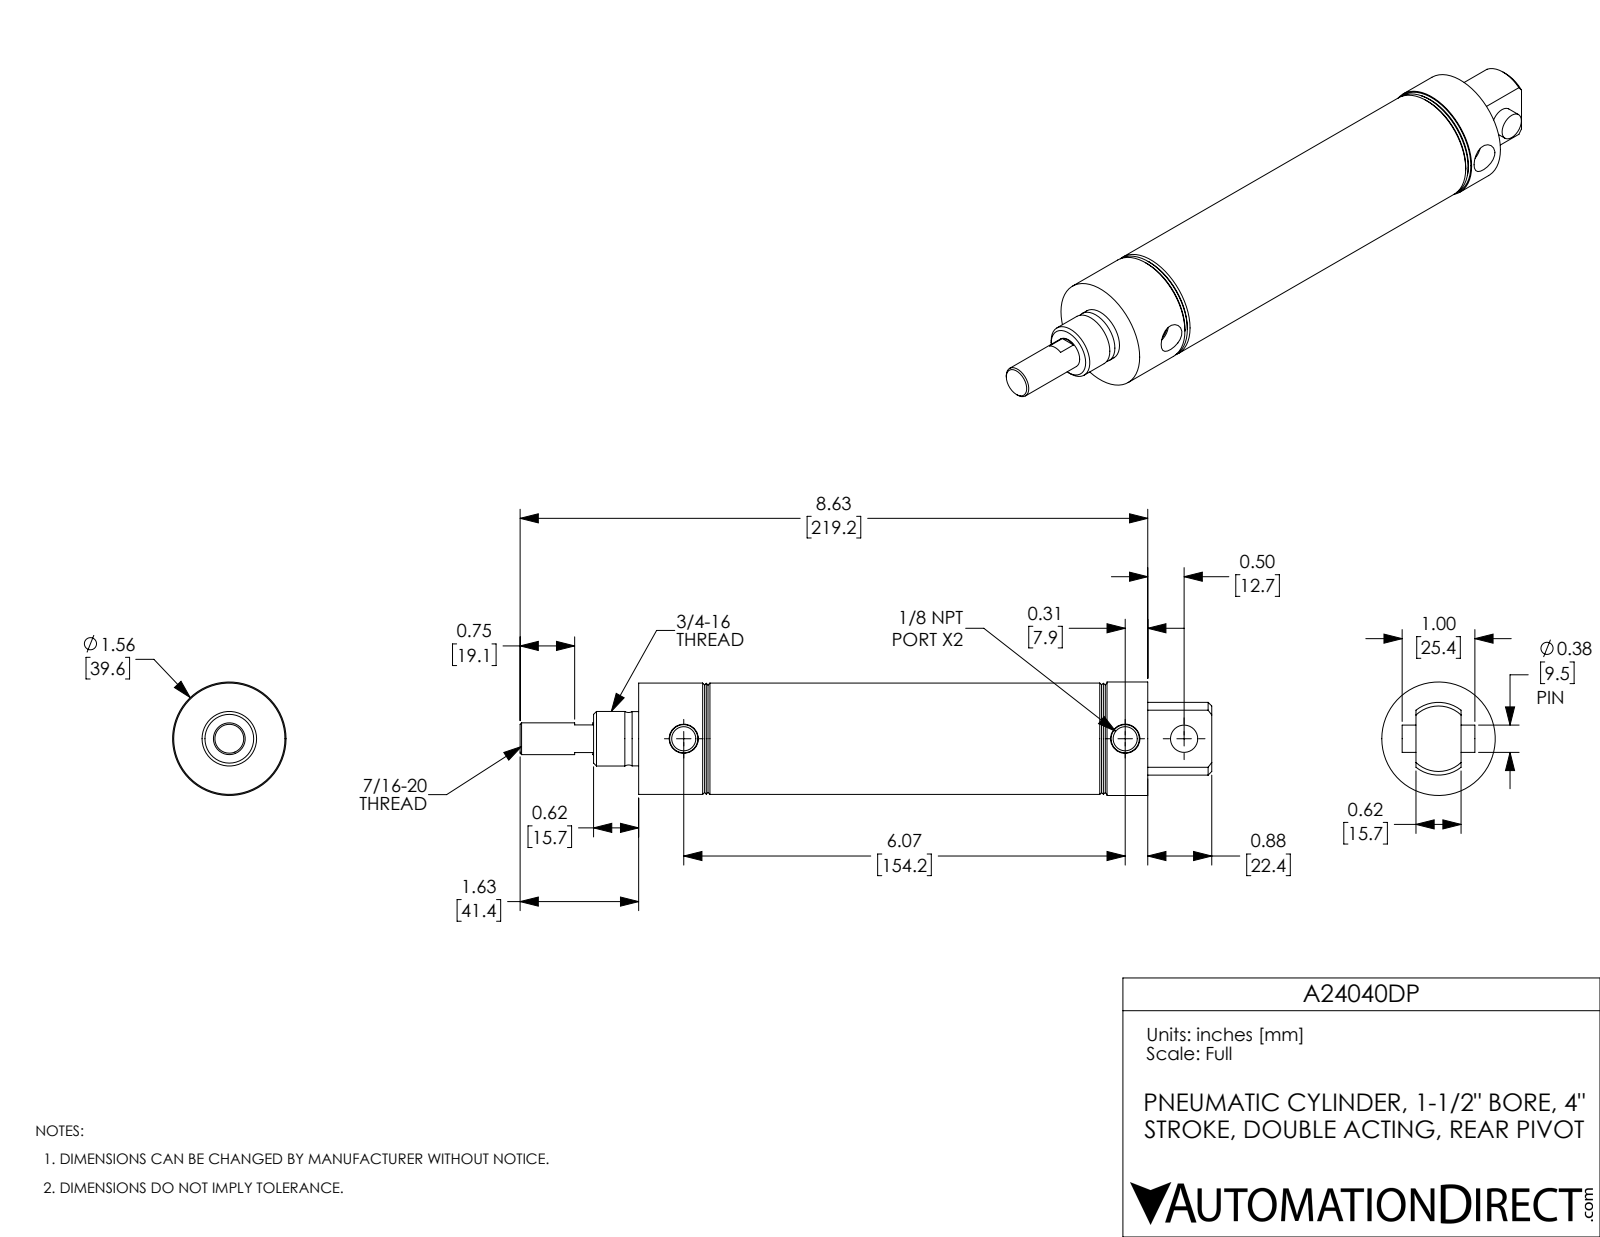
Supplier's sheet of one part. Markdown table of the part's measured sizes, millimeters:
| quantity | value |
| --- | --- |
| part name | A24040DP-MainBody; A24040DP-Rod; A24040DP-Pin; A24040DP |
| STEP written by | SolidWorks 2017 (AUTOMOTIVE_DESIGN) |
| units | millimeters |
| bodies | 3 solids, 84 faces (22 planar, 28 cylindrical, 34 other) |
| overall size | 241.6 × 39.6 × 39.6 |
| volume | 119 500 mm³ |
| surface area | 56 170 mm² |
| round holes (diameter × count) | 8.4 × 2, 9.5 × 1, 11.1 × 1, 38.1 × 1 |
| round bosses / shafts (diameter × count) | 39.6 × 1, 38.9 × 1, 19.1 × 1, 18.9 × 1 |
| partial cylindrical surfaces (radius × count) | 12.7 × 1 |
| main face-to-face distances | 31.8, 146.1, 114.3, 12.7, 101.6, 133.4, 44.5, 177.8, 15.7, 22.4 |
| hole center spacings | 20.6, 154.2, 174.8 |
